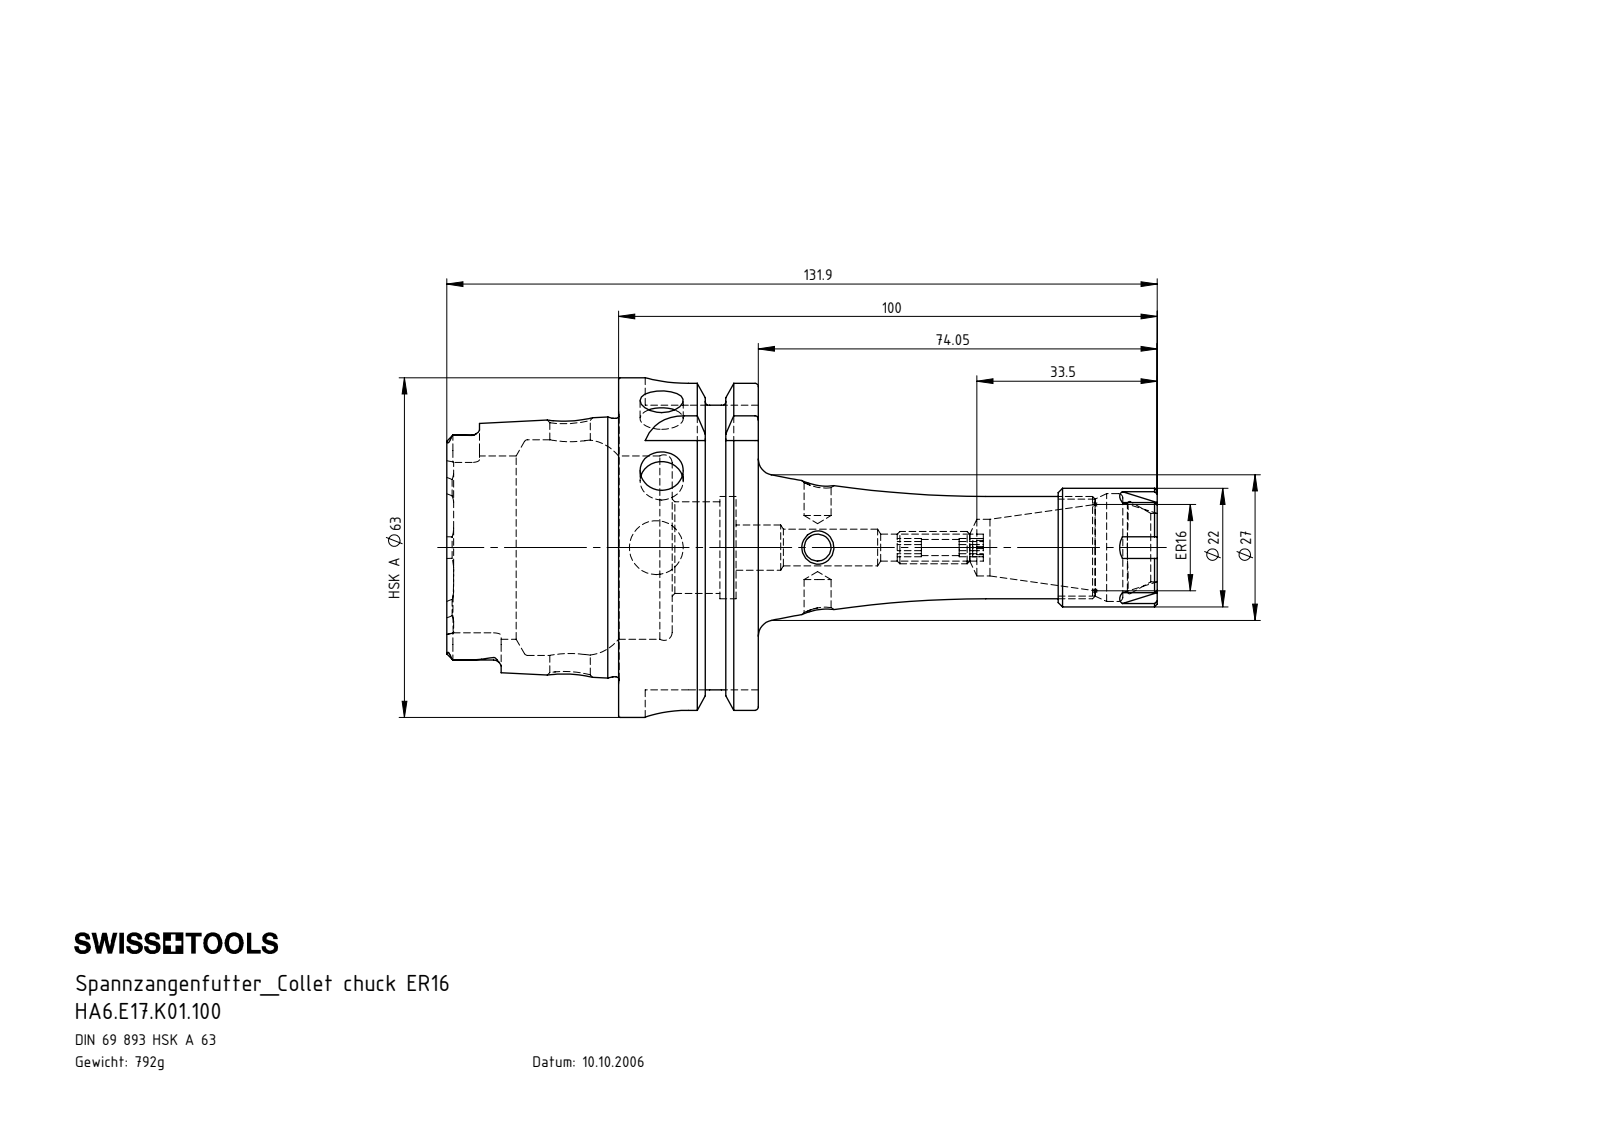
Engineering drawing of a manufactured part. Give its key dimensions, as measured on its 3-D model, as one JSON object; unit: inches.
{"part_name": "HA6.E17.K01.100; ERU-AN2.K01.016_A; E17-ER1.001.018; HA6-E17.K01.100_B_Fertigbearbeitung", "step_written_by": "SolidWorks 2012 (CONFIG_CONTROL_DESIGN)", "units": "inches", "bodies": {"solids": 3, "faces": 307, "planar": 105, "cylindrical": 80, "other": 122}, "overall_size": [5.193, 2.48, 2.48], "volume_in3": 6.156, "surface_area_in2": 48.65, "round_holes": [[0.197, 3], [0.315, 2], [0.118, 1], [0.268, 1], [0.295, 1], [0.331, 1], [0.394, 1], [0.413, 1], [0.5, 1], [0.669, 1], [0.709, 1], [0.748, 1]], "round_bosses_or_shafts": [[2.48, 1], [2.163, 1], [1.887, 1], [0.866, 1], [0.236, 1]], "partial_cylinders_radius": [[0.055, 6], [0.113, 4], [0.315, 4], [0.303, 2]], "face_to_face_distances": [1.022, 0.63, 0.392, 1.256, 1.648, 2.278, 2.079, 0.858, 0.467, 2.114], "hole_center_spacings": [1.179, 1.809]}
